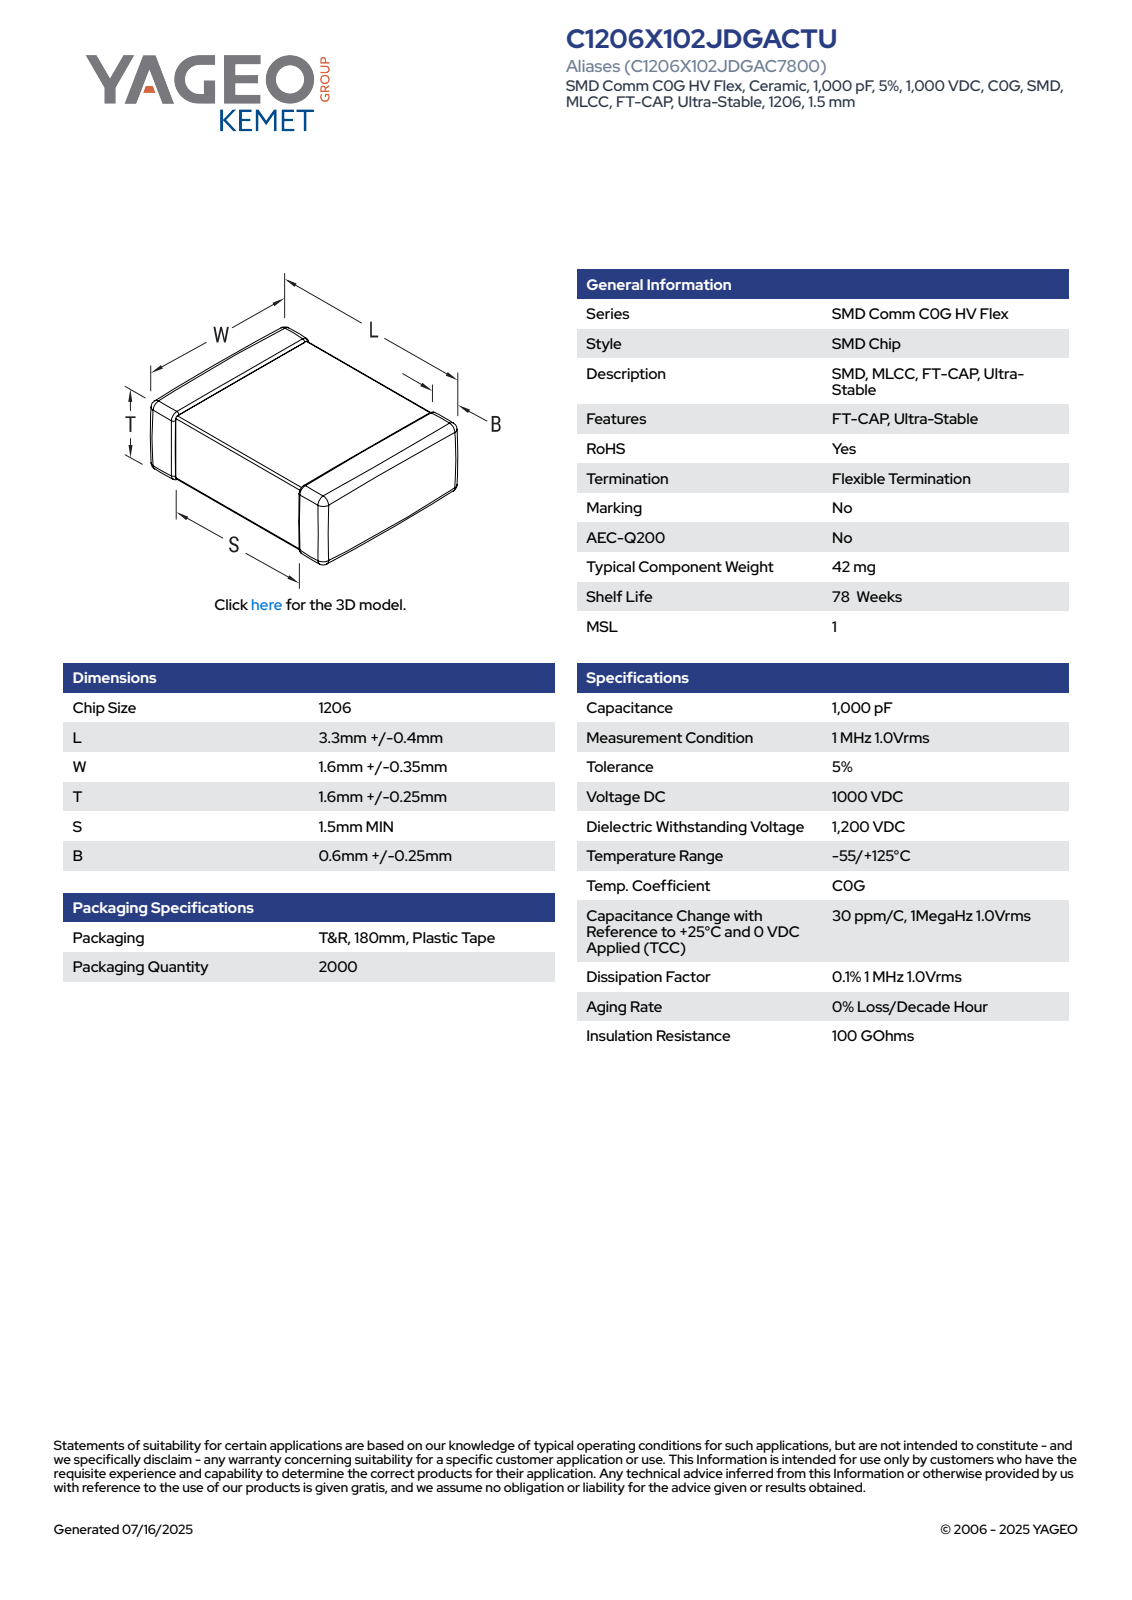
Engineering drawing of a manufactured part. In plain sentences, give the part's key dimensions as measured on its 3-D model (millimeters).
The part is named "CCS_CCSTD_1206_L3.7W1.95T1.85B0.6". Its 3-D file was written by "SolidWorks 2021 (AUTOMOTIVE_DESIGN)". It is 4 solids with 125 faces: 71 planar, 38 cylindrical and 16 other. Overall it measures 3.7 by 1.95 by 1.85 millimeters. Its volume is 13 cubic millimeters and its surface area 35 square millimeters. The main face-to-face distances are 1.81, 1.91, 1.77, 1.87, 3.7, 1.85, 1.95, 1.71, 1.99, 2.
